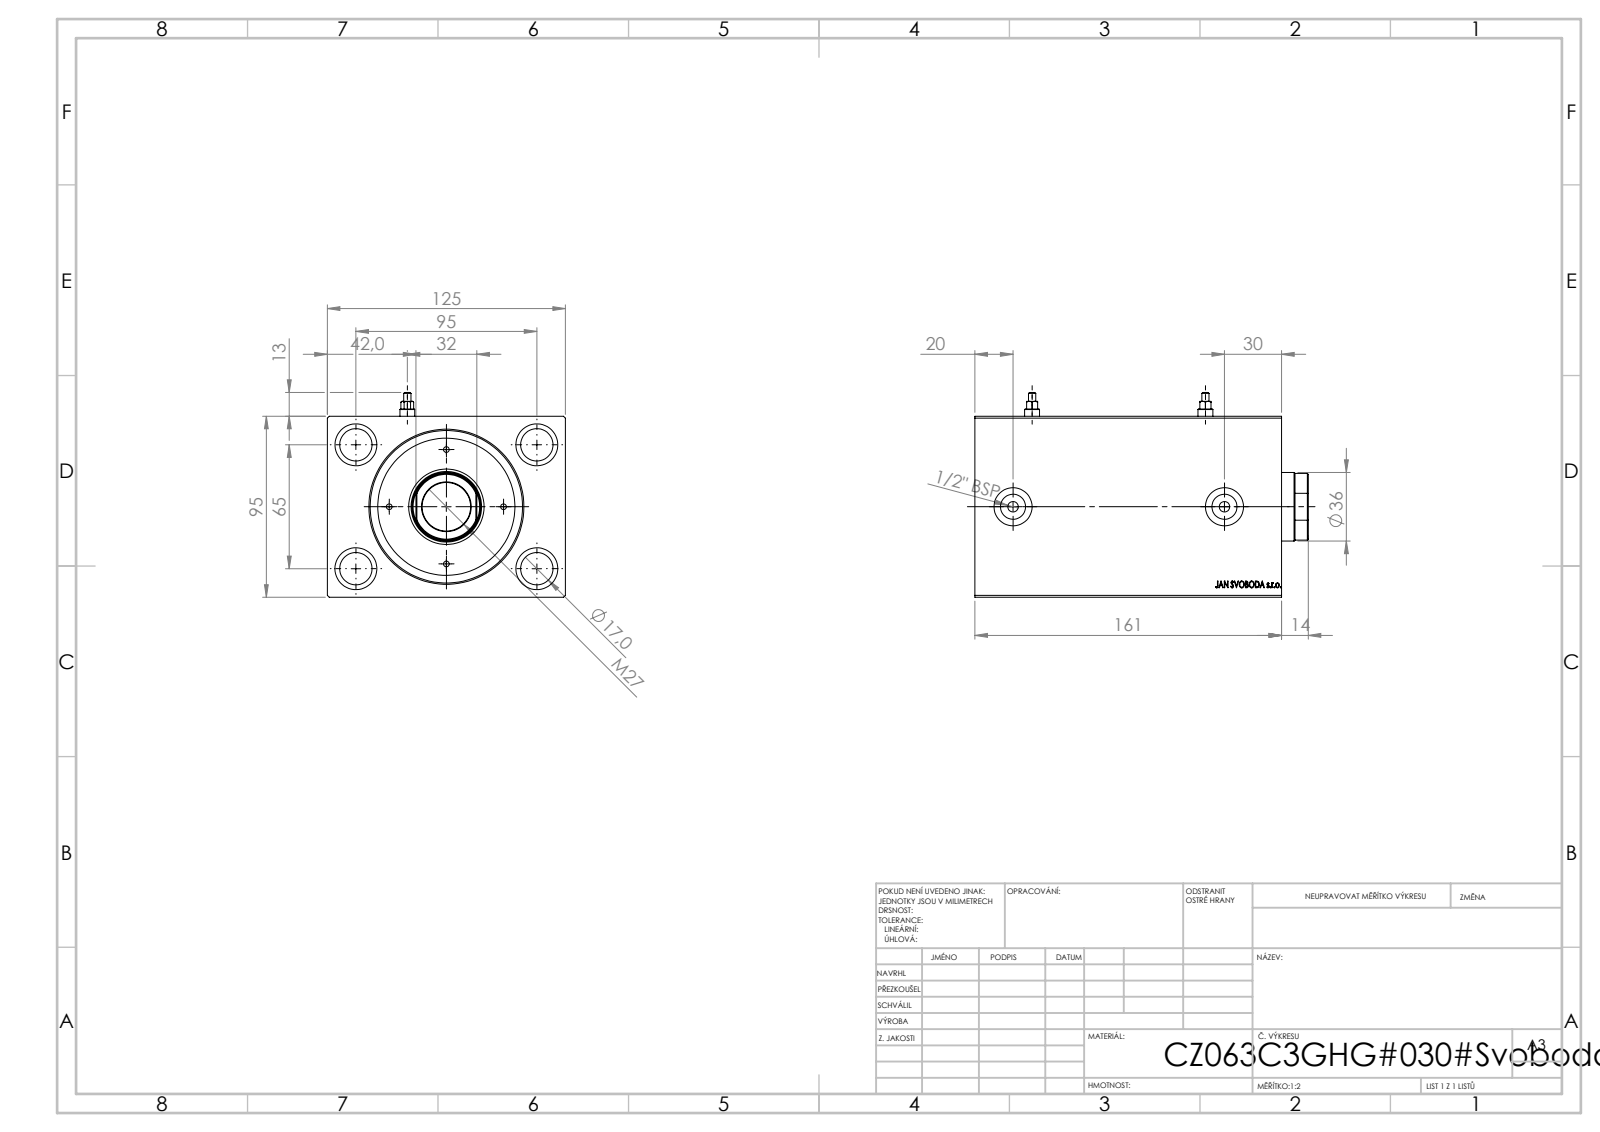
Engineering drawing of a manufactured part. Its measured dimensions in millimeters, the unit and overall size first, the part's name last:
Units: millimetres
Overall size (bounding box): 161 × 125 × 95
Round holes (diameter × count): ⌀17 ×4, ⌀22 ×4, ⌀5.5 ×2, ⌀8 ×2, ⌀13.16 ×2, ⌀20 ×2, ⌀36 ×1, ⌀63 ×1, ⌀80 ×1
Main face-to-face distances: 95, 125, 161, 140.2, 20.8, 14, 126.2, 147, 10.33, 150.67
Hole centre spacings: 57.55, 65, 95, 115.11, 91, 111
Volume: 1 285 000 mm³ · Surface area: 158 073 mm²
Bodies: 1 solid, 825 faces (397 planar, 46 cylindrical, 382 other)
STEP written by: SolidWorks 2019 (CONFIG_CONTROL_DESIGN)
